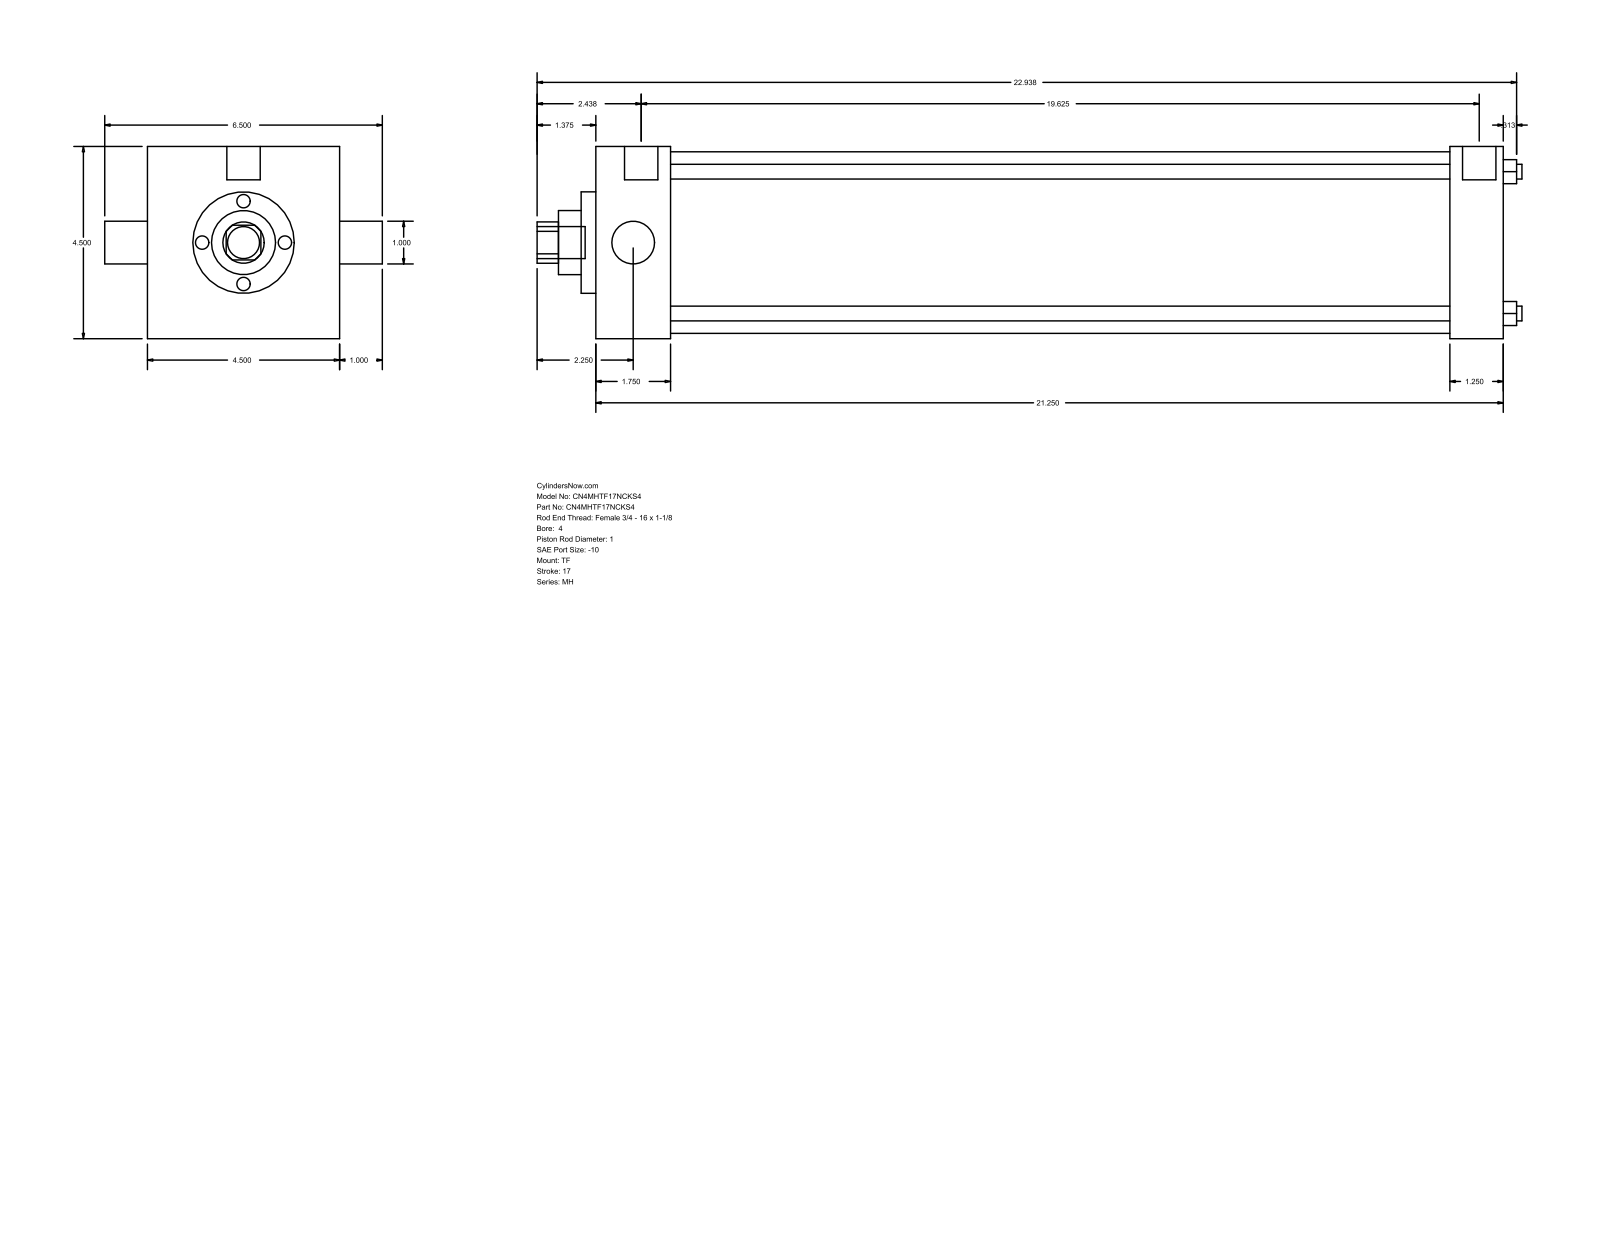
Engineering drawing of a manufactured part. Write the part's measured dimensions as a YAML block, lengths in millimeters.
part_name: "MH_TF__0400_1"
step_written_by: "GSSL Pune (CONFIG_CONTROL_DESIGN)"
units: millimeters
bodies: {solids: 0, faces: 86, planar: 61, cylindrical: 25, other: 0}
overall_size: [585.79, 165.1, 114.3]
round_holes:
  - {diameter: 8.76, count: 4}
  - {diameter: 25.4, count: 2}
  - {diameter: 38.1, count: 1}
  - {diameter: 60.33, count: 1}
  - {diameter: 107.95, count: 1}
round_bosses_or_shafts:
  - {diameter: 8.73, count: 3}
  - {diameter: 19.84, count: 2}
  - {diameter: 19.05, count: 1}
partial_cylinders:
  - {radius: 12.29, count: 1}
face_to_face_distances: [114.3, 539.75, 44.46, 495.29, 508, 463.54, 31.75, 8.73, 53.19, 516.73]
hole_center_spacings: [59.62, 84.32, 119.25]
